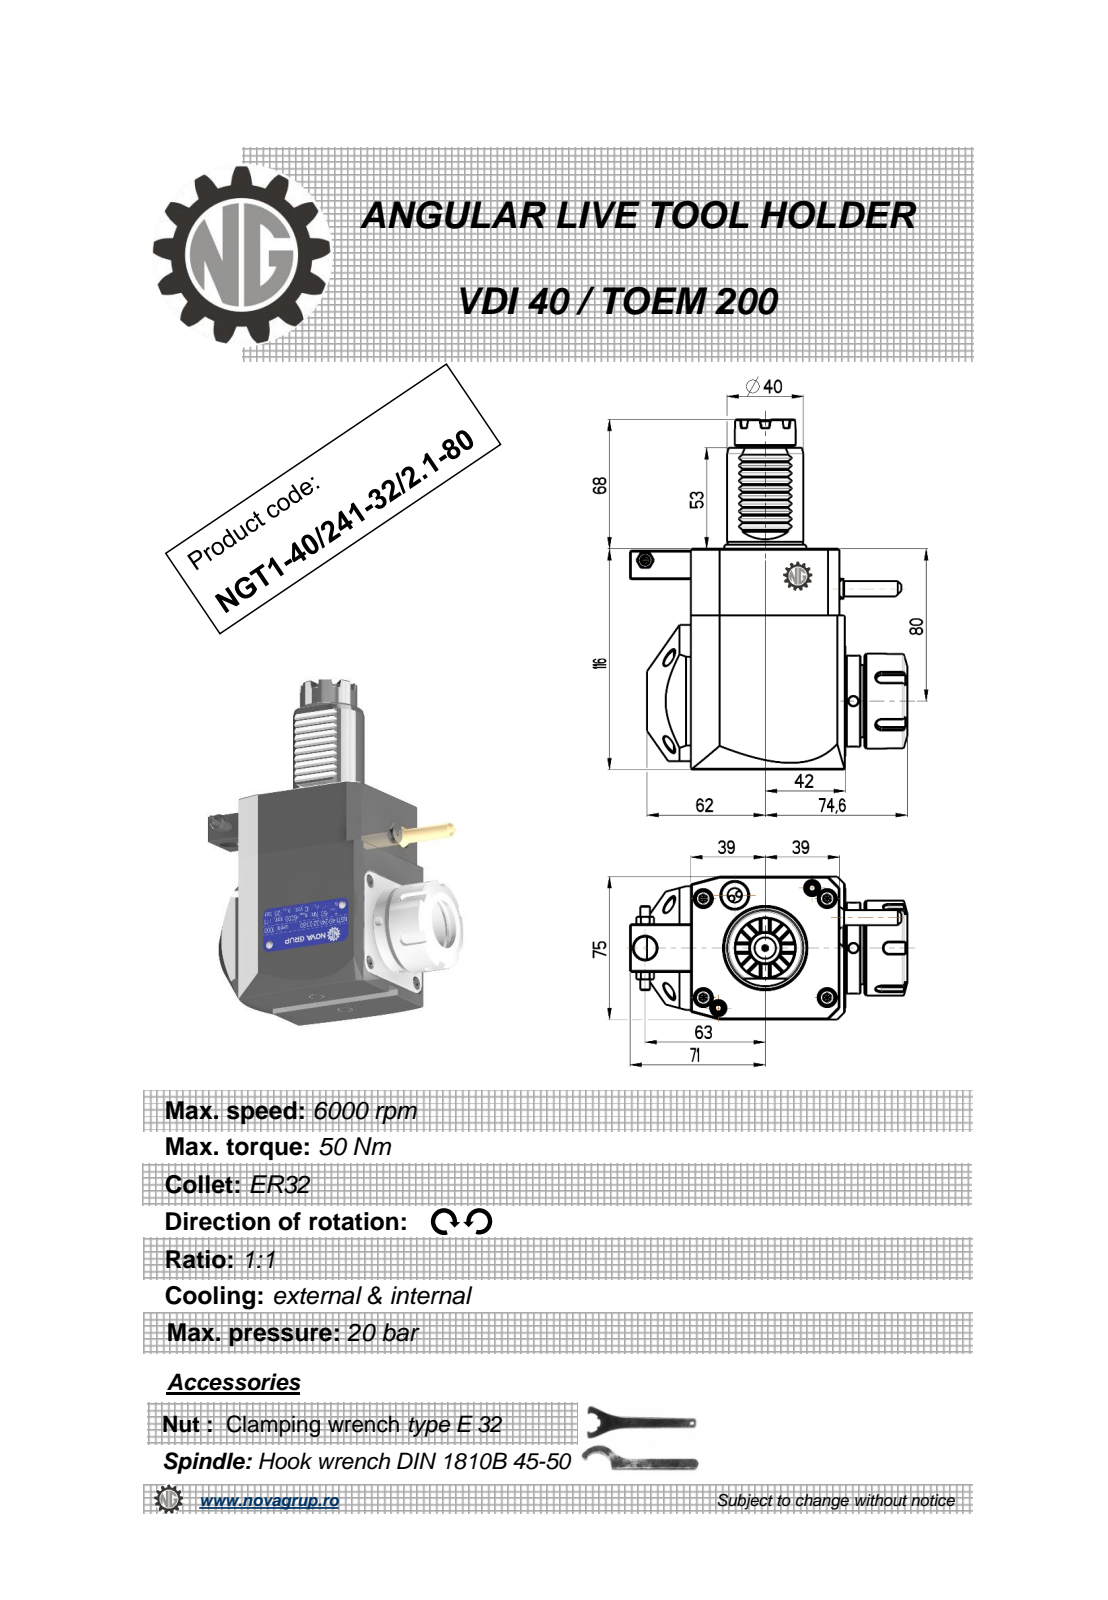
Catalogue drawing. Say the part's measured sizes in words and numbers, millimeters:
The part is named "NGT1_40_241_32_2_1_80". Its 3-D file was written by "PRO/ENGINEER BY PARAMETRIC TECHNOLOGY CORPORATION, 2010280 (CONFIG_CONTROL_DESIGN)". It is 1 solid with 491 faces: 227 planar, 97 cylindrical and 167 other. Overall it measures 184 by 145.6 by 76.6 millimeters. Its volume is 889 705 cubic millimeters and its surface area 71 990 square millimeters. Round holes: 3 of diameter 5, 1 of diameter 3, 1 of diameter 4.2, 1 of diameter 9.5, 1 of diameter 12, 1 of diameter 27. Round bosses or shafts: 1 of diameter 50, 1 of diameter 48, 1 of diameter 41, 1 of diameter 40, 1 of diameter 32, 1 of diameter 17, 1 of diameter 11.2, 1 of diameter 8.96. Partial cylindrical surfaces (rounded edges, fillets, slot ends): 12 of radius 0.26, 10 of radius 0.3, 6 of radius 0.22, 5 of radius 3, 1 of radius 0.5, 1 of radius 8.6, 1 of radius 40. The main face-to-face distances are 75, 116, 81, 78, 3, 80.8, 2.8, 112, 25, 4.5. The hole center spacings are 20.93, 61.13, 72.5, 109.25, 131.95.
